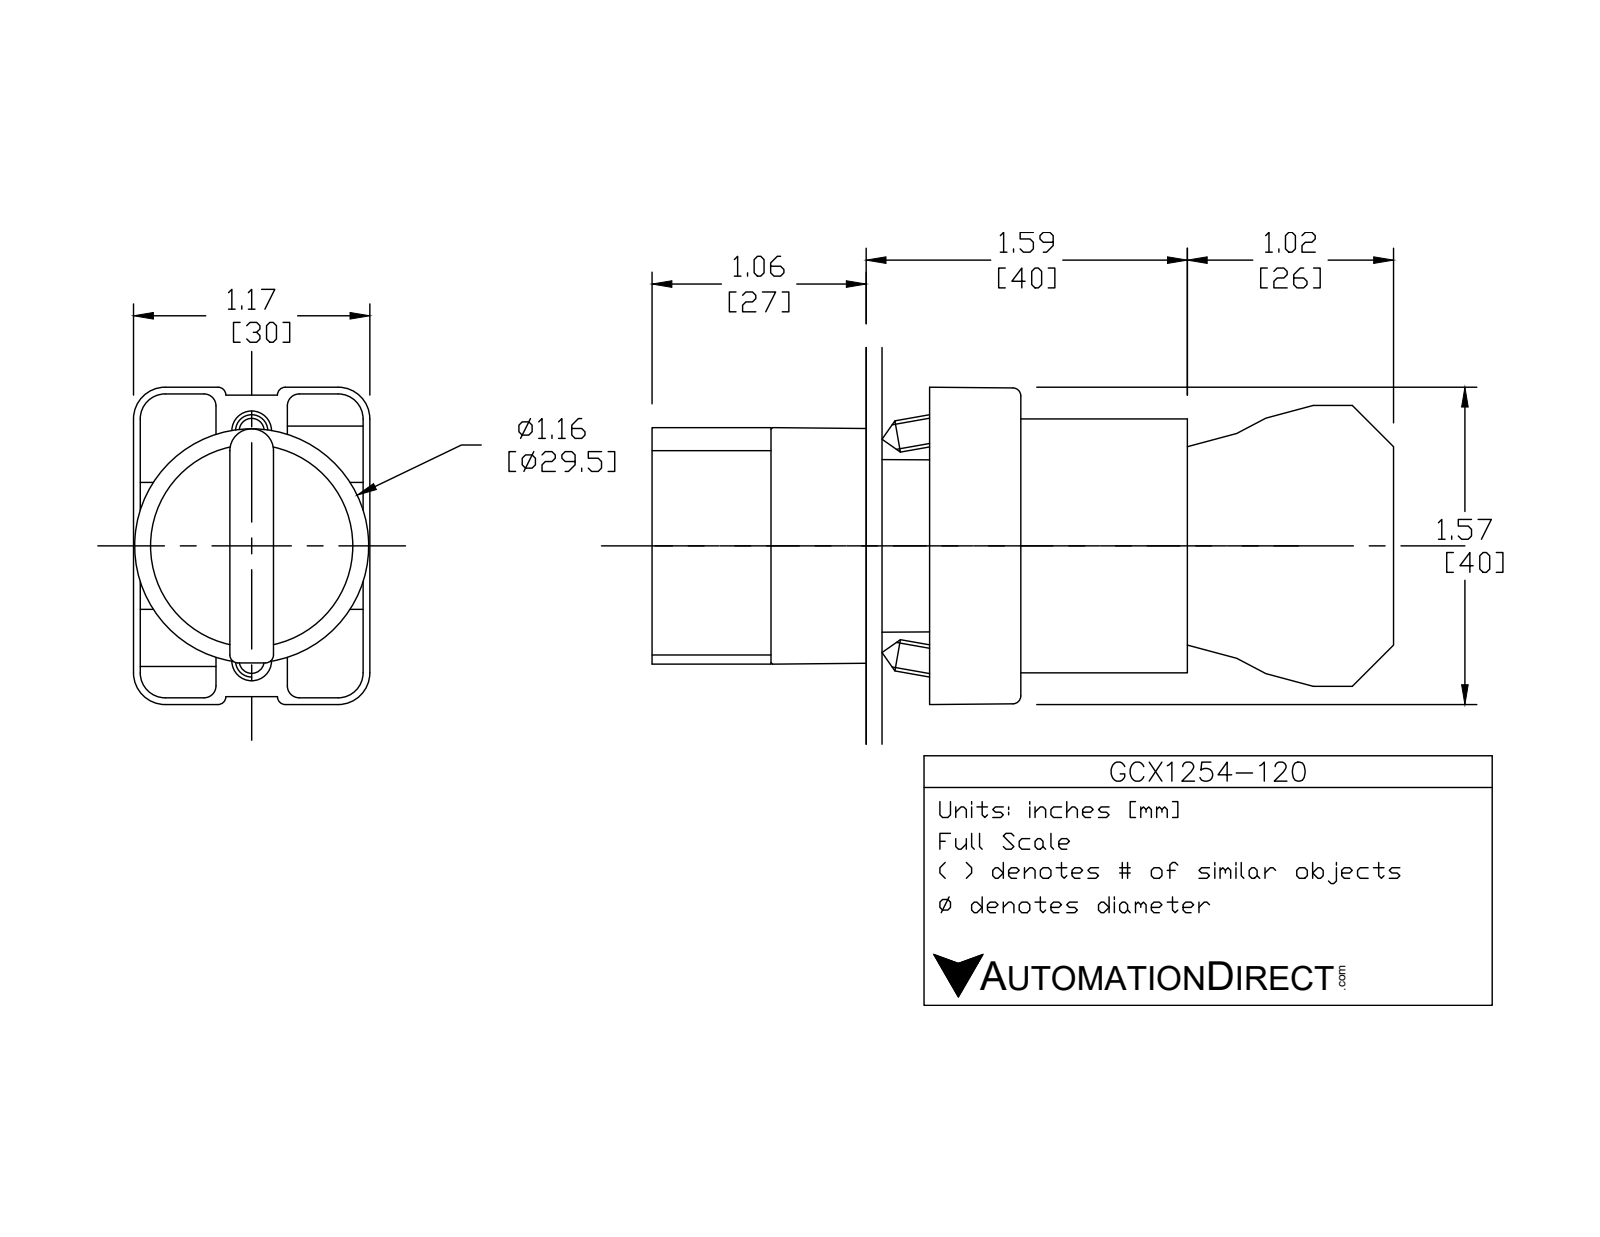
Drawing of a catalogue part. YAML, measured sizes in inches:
part_name: "GCX1254 OPERATOR; GCX1254-120; ECX1050; ecx1040 (+1 more)"
step_written_by: "SolidWorks 2016 (AUTOMOTIVE_DESIGN)"
units: inches
bodies: {solids: 8, faces: 445, planar: 263, cylindrical: 151, other: 31}
overall_size: [3.653, 1.581, 1.177]
volume: 2.799
surface_area: 39
round_holes:
  - {diameter: 0.079, count: 2}
  - {diameter: 0.124, count: 2}
  - {diameter: 0.13, count: 2}
  - {diameter: 0.087, count: 1}
  - {diameter: 0.197, count: 1}
  - {diameter: 0.469, count: 1}
  - {diameter: 0.878, count: 1}
  - {diameter: 0.888, count: 1}
  - {diameter: 1.024, count: 1}
round_bosses_or_shafts:
  - {diameter: 0.157, count: 4}
  - {diameter: 1.175, count: 1}
  - {diameter: 1.004, count: 1}
  - {diameter: 0.945, count: 1}
  - {diameter: 0.856, count: 1}
  - {diameter: 0.78, count: 1}
  - {diameter: 0.504, count: 1}
partial_cylinders:
  - {radius: 0.059, count: 24}
  - {radius: 0.041, count: 12}
  - {radius: 0.124, count: 12}
  - {radius: 0.157, count: 12}
  - {radius: 0.039, count: 9}
  - {radius: 0.128, count: 2}
  - {radius: 0.02, count: 1}
  - {radius: 0.063, count: 1}
face_to_face_distances: [0.827, 2.02, 1.193, 0.579, 1.244, 1.171, 0.472, 0.469, 0.031, 0.033]
hole_center_spacings: [0.236, 0.544, 0.472, 0.49]
